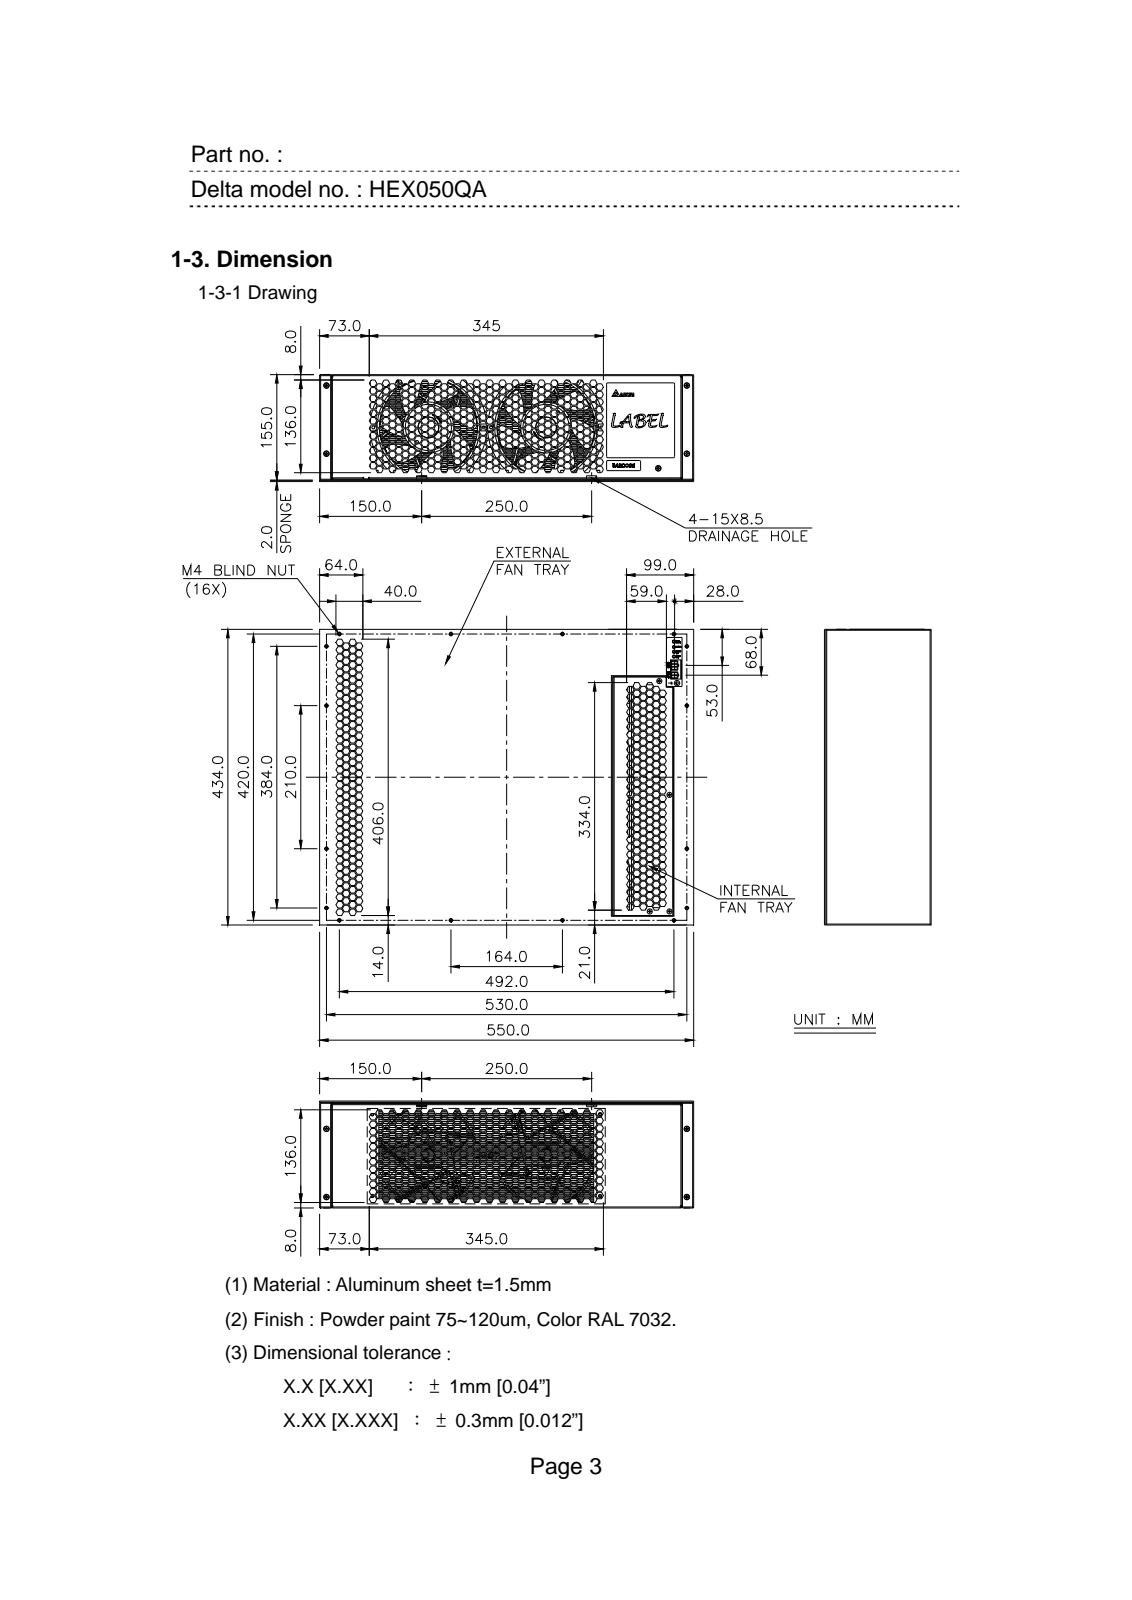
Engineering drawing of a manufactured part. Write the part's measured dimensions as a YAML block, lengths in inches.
part_name: "HEX050QA"
step_written_by: "SolidWorks 2011 (CONFIG_CONTROL_DESIGN)"
units: inches
bodies: {solids: 1, faces: 79, planar: 47, cylindrical: 32, other: 0}
overall_size: [21.654, 17.087, 6.26]
volume: 2234
surface_area: 1231
round_holes:
  - {diameter: 0.157, count: 16}
face_to_face_distances: [6.102, 0.118, 16.969, 21.654, 16.85, 17.087, 5.984, 0.315, 5.669, 5.354]
hole_center_spacings: [6.457, 17.751, 1.03, 3.425, 4.201, 7.239, 8.306, 11.693]
